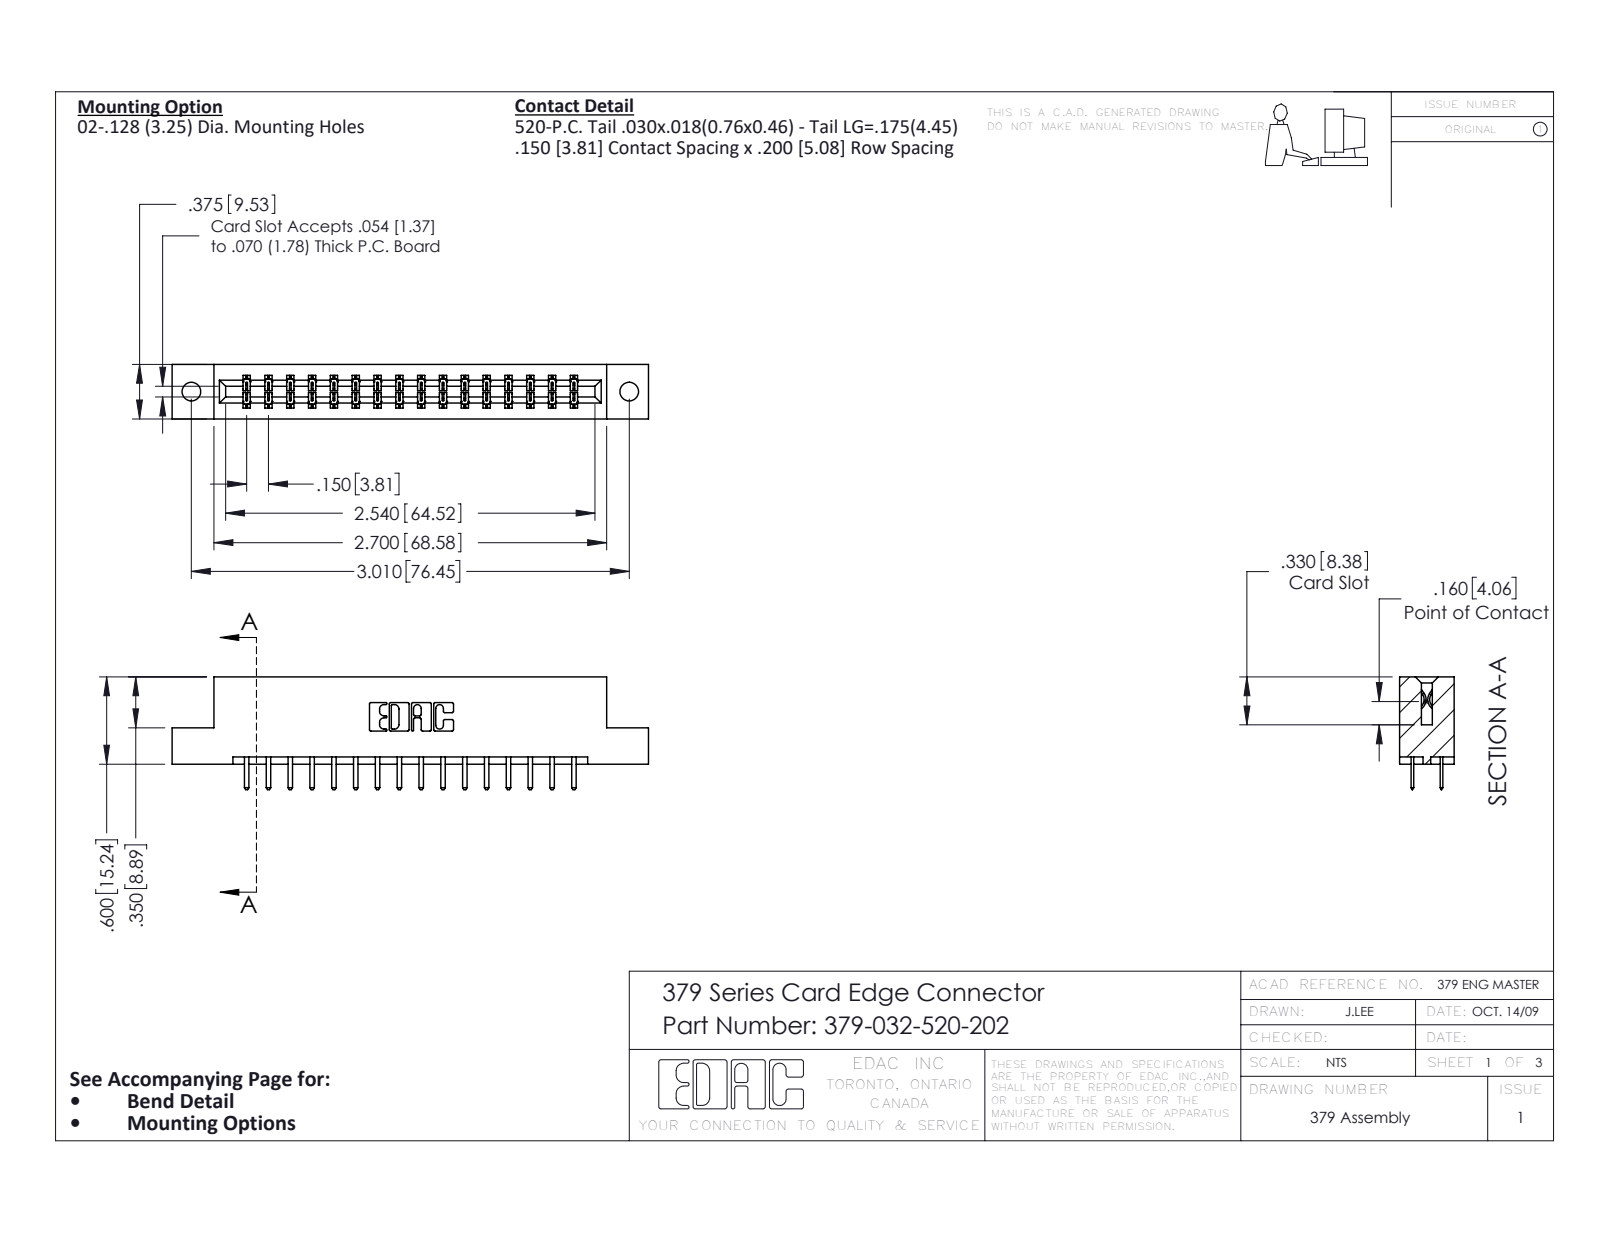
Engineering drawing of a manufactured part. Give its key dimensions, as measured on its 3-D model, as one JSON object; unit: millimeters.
{"part_name": "379 Part_Flush - .128 Dia; 379-032-520-202; 345-292-001_345-293-120", "step_written_by": "SolidWorks 2020 (CONFIG_CONTROL_DESIGN)", "units": "millimeters", "bodies": {"solids": 33, "faces": 1906, "planar": 1286, "cylindrical": 620, "other": 0}, "overall_size": [83.2, 19.7, 9.5], "volume_mm3": 8490, "surface_area_mm2": 8974, "round_holes": [[3.3, 2]], "partial_cylinders_radius": [[0.2, 48], [0.3, 36], [0.3, 22], [0.2, 6], [0.8, 6], [0.7, 3], [0.4, 2], [0.6, 2]], "face_to_face_distances": [7.6, 5.1, 9.5, 1.9, 2.5, 3.8, 1.3, 15.2, 5.7, 14], "hole_center_spacings": [76.5]}
